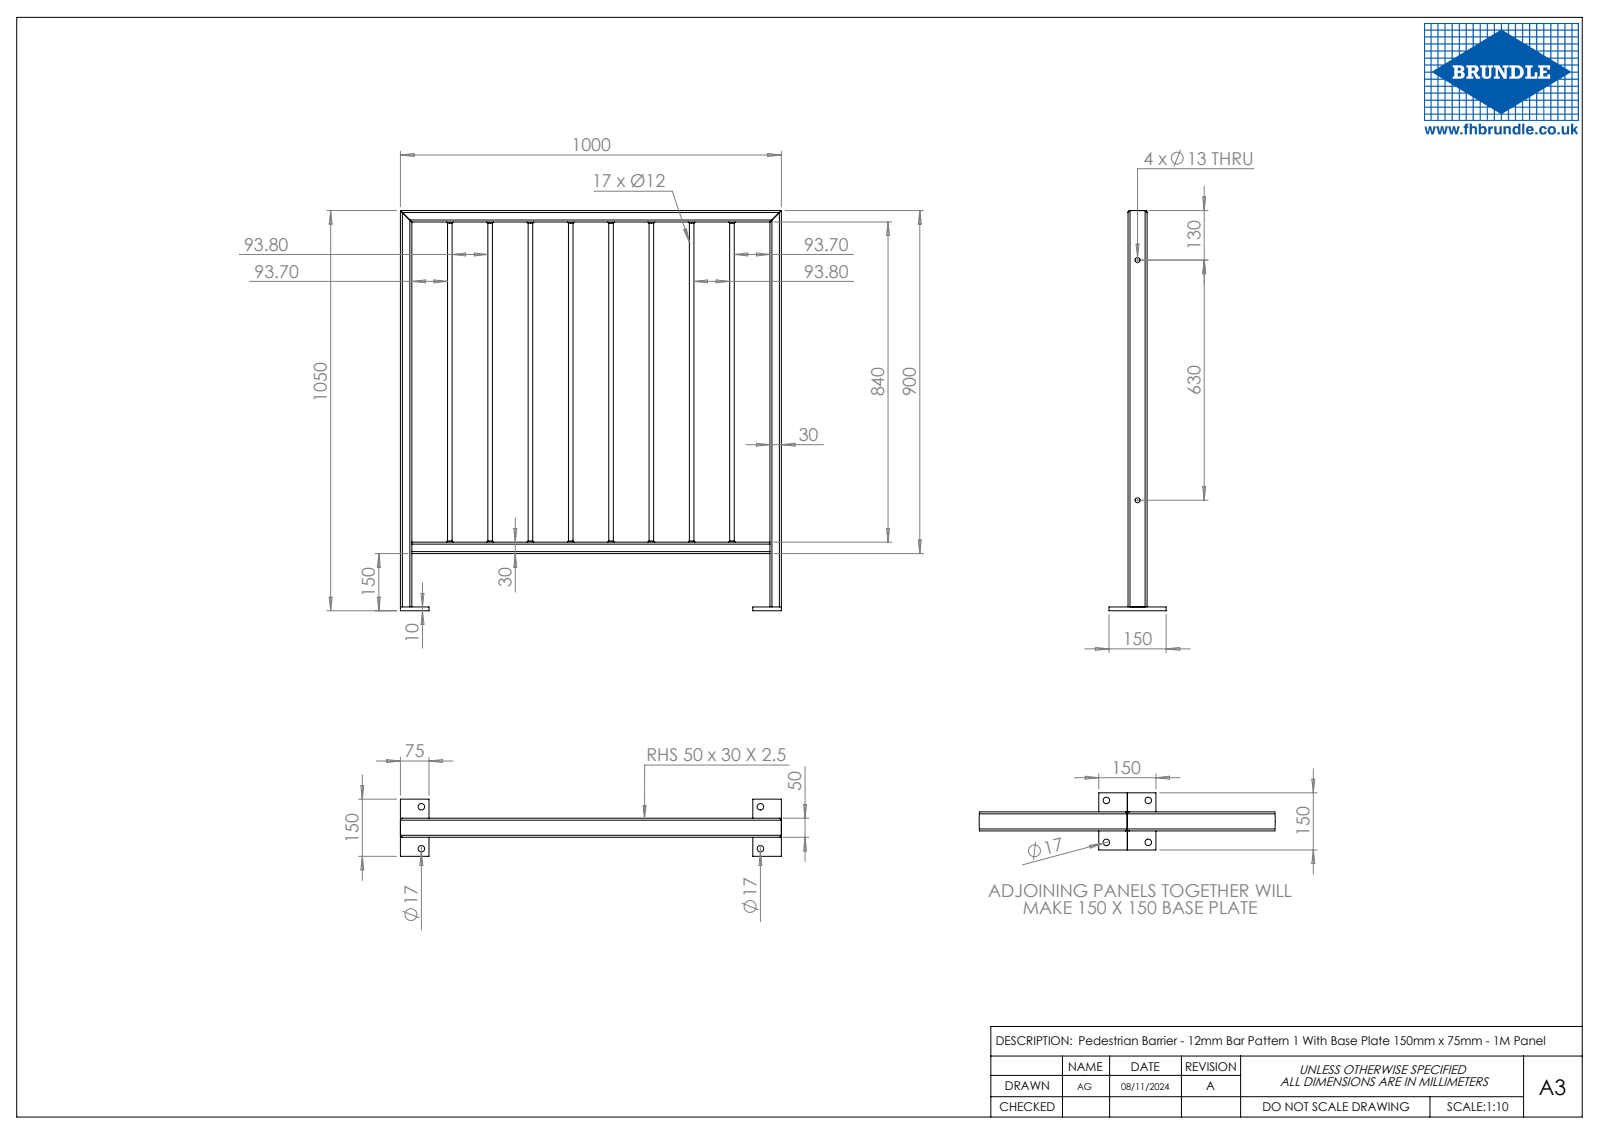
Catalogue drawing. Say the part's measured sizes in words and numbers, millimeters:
The part is named "220015B". Its 3-D file was written by "SolidWorks 2023 (CONFIG_CONTROL_DESIGN)". It is 30 solids with 220 faces: 84 planar, 104 cylindrical and 32 other. Overall it measures 1050 by 1000 by 150 millimeters. Its volume is 2 448 000 cubic millimeters and its surface area 1 451 000 square millimeters. Round holes: 8 of diameter 12, 4 of diameter 17, 2 of diameter 13. Partial cylindrical surfaces (rounded edges, fillets, slot ends): 16 of radius 2.6, 16 of radius 5.2. The main face-to-face distances are 2.6, 27.4, 970, 30, 47.4, 24.8, 870, 997.4, 50, 967.4. The hole center spacings are 105.8, 211.6, 317.4, 92.76, 188.69, 291.54, 395.94, 423.2.
